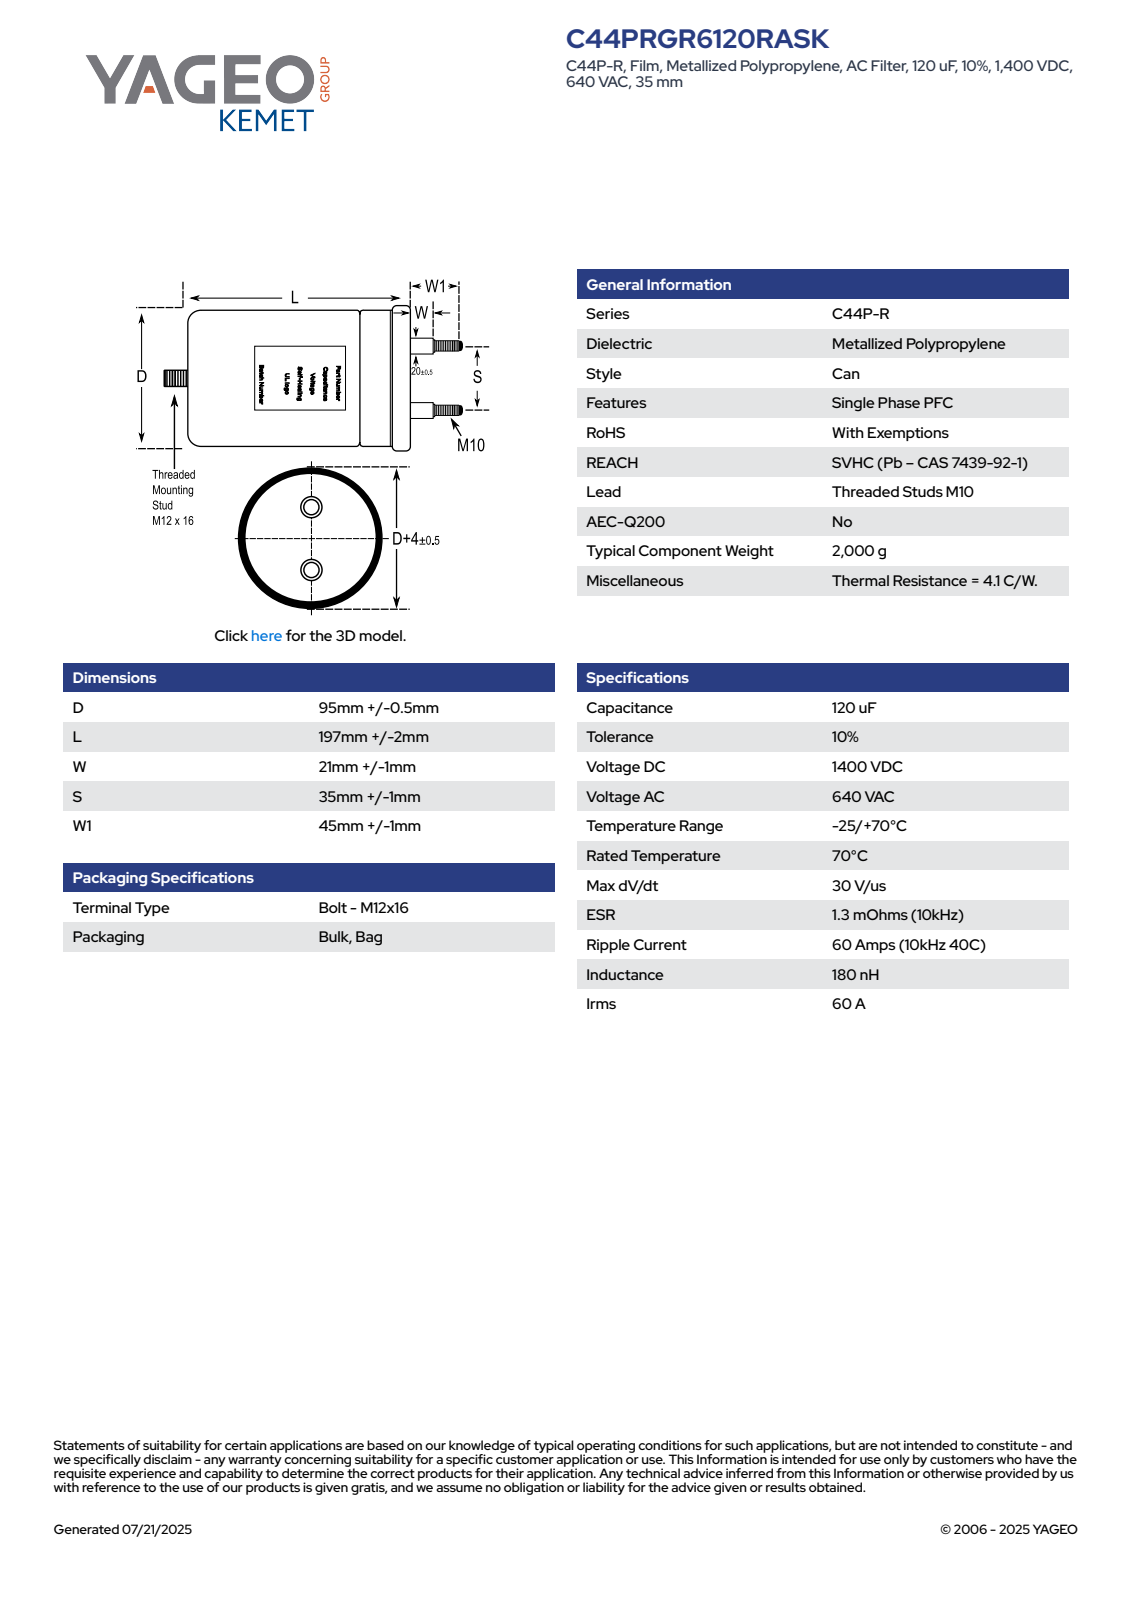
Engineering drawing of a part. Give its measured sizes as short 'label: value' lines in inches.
name: CFP_C44P_95X247_D95.5L199S35
written by: SolidWorks 2014 (AUTOMOTIVE_DESIGN)
unit: in
bodies: 1 solid, 105 faces (32 planar, 36 cylindrical, 37 other)
size: 10.276 × 3.937 × 3.937
volume: 88.36 in³; area: 123.2 in²
bosses: 3× ⌀0.472, 2× ⌀0.807, 2× ⌀0.394, 1× ⌀3.937, 1× ⌀3.76
rounds: 1× R1.88
face distances: 7.835, 8.661, 0.827, 7.583, 0.252, 1.078, 9.646, 2.063, 1.811, 0.984
